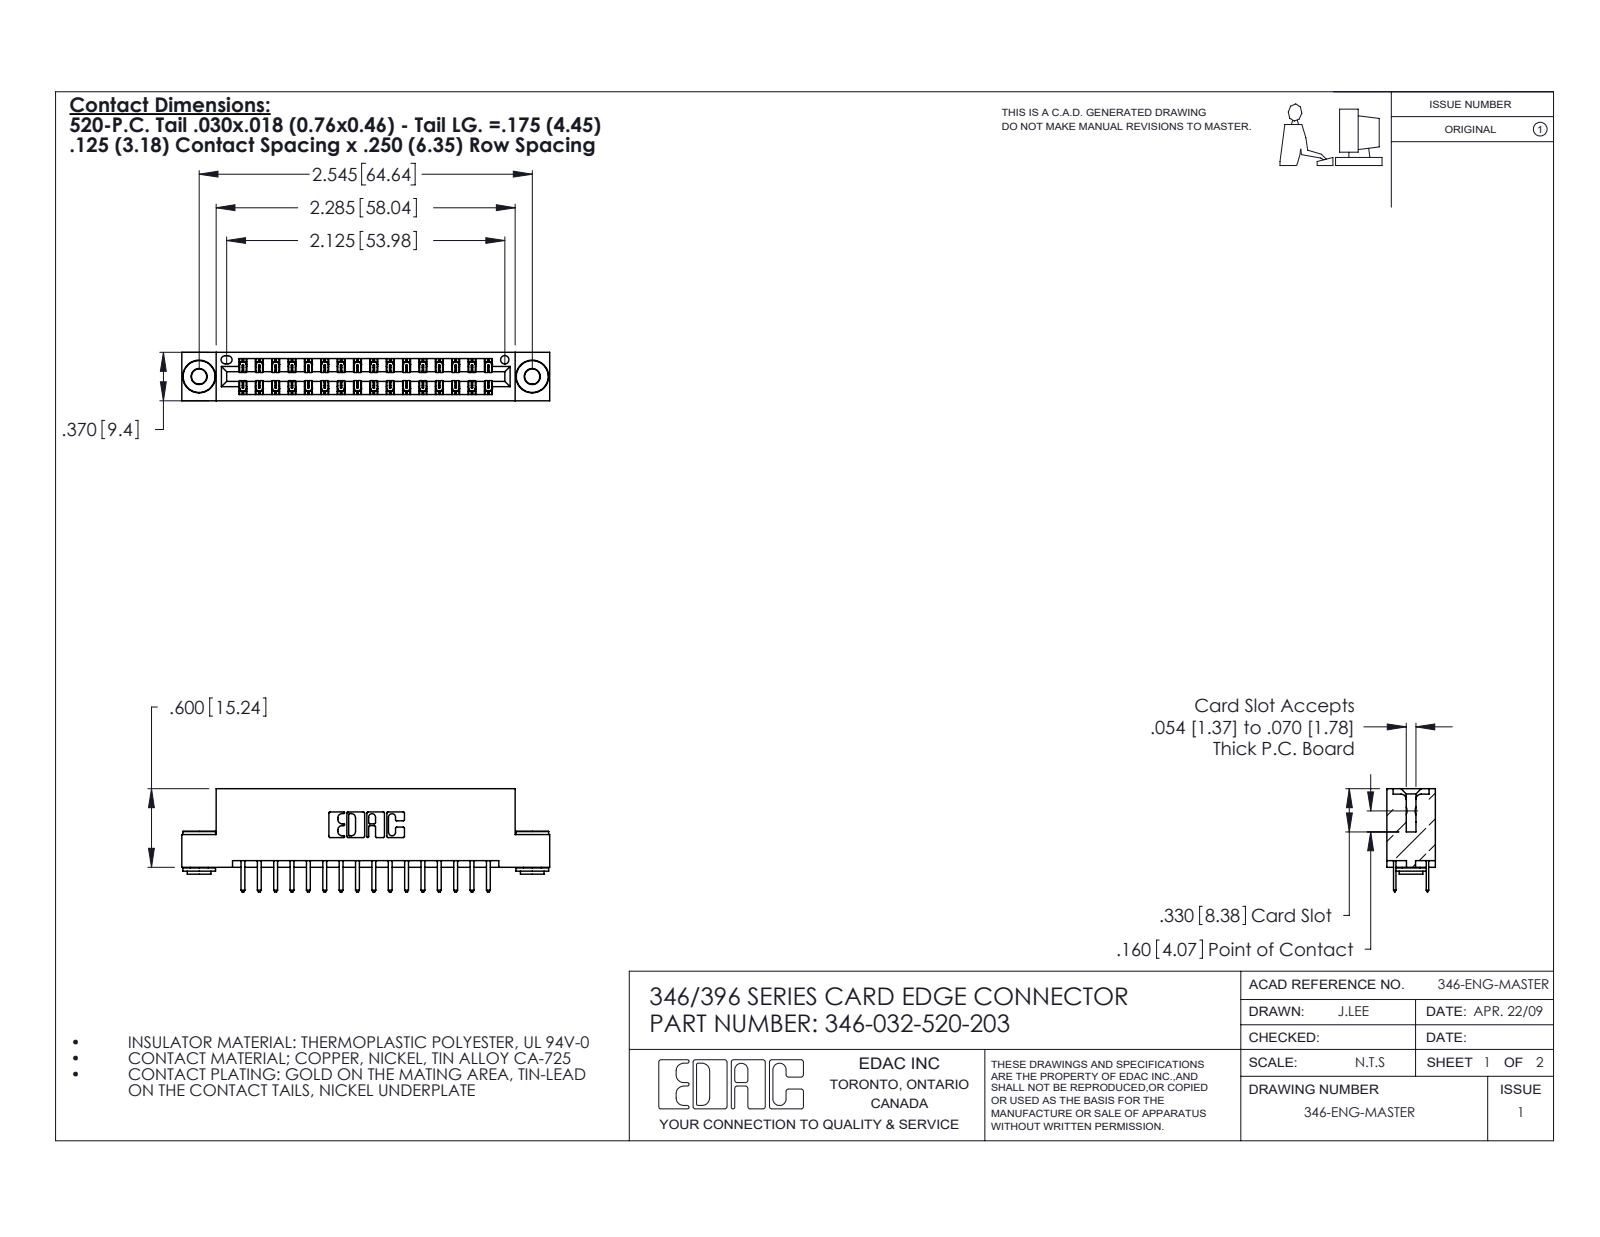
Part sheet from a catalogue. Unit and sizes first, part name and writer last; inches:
Units: inches
Overall size (bounding box): 2.81 × 0.788 × 0.37
Round holes (diameter × count): ⌀0.116 ×2, ⌀0.156 ×2, ⌀0.064 ×1
Round bosses / shafts (diameter × count): ⌀0.25 ×2, ⌀0.18 ×2, ⌀0.136 ×2
Partial cylindrical surfaces — rounded edges, fillets, slot ends (radius × count): R0.006 ×48, R0.01 ×36, R0.01 ×22, R0.007 ×6, R0.031 ×6, R0.026 ×3, R0.014 ×2, R0.022 ×2
Main face-to-face distances: 0.25, 0.048, 0.322, 0.37, 0.025, 0.275, 0.072, 0.298, 0.148, 0.222
Hole centre spacings: 0.246, 2.338, 2.545
Volume: 0.412 in³ · Surface area: 14.07 in²
Bodies: 35 solids, 1966 faces (1284 planar, 674 cylindrical, 8 other)
Part name (STEP PRODUCT): 345-292-001_345-293-120; 346-032-520-203; 346 Part_Flush Mounting Lugs - 0.156 Dia-TH; 345-250-002_345-250-002-102
STEP written by: SolidWorks 2020 (CONFIG_CONTROL_DESIGN)
